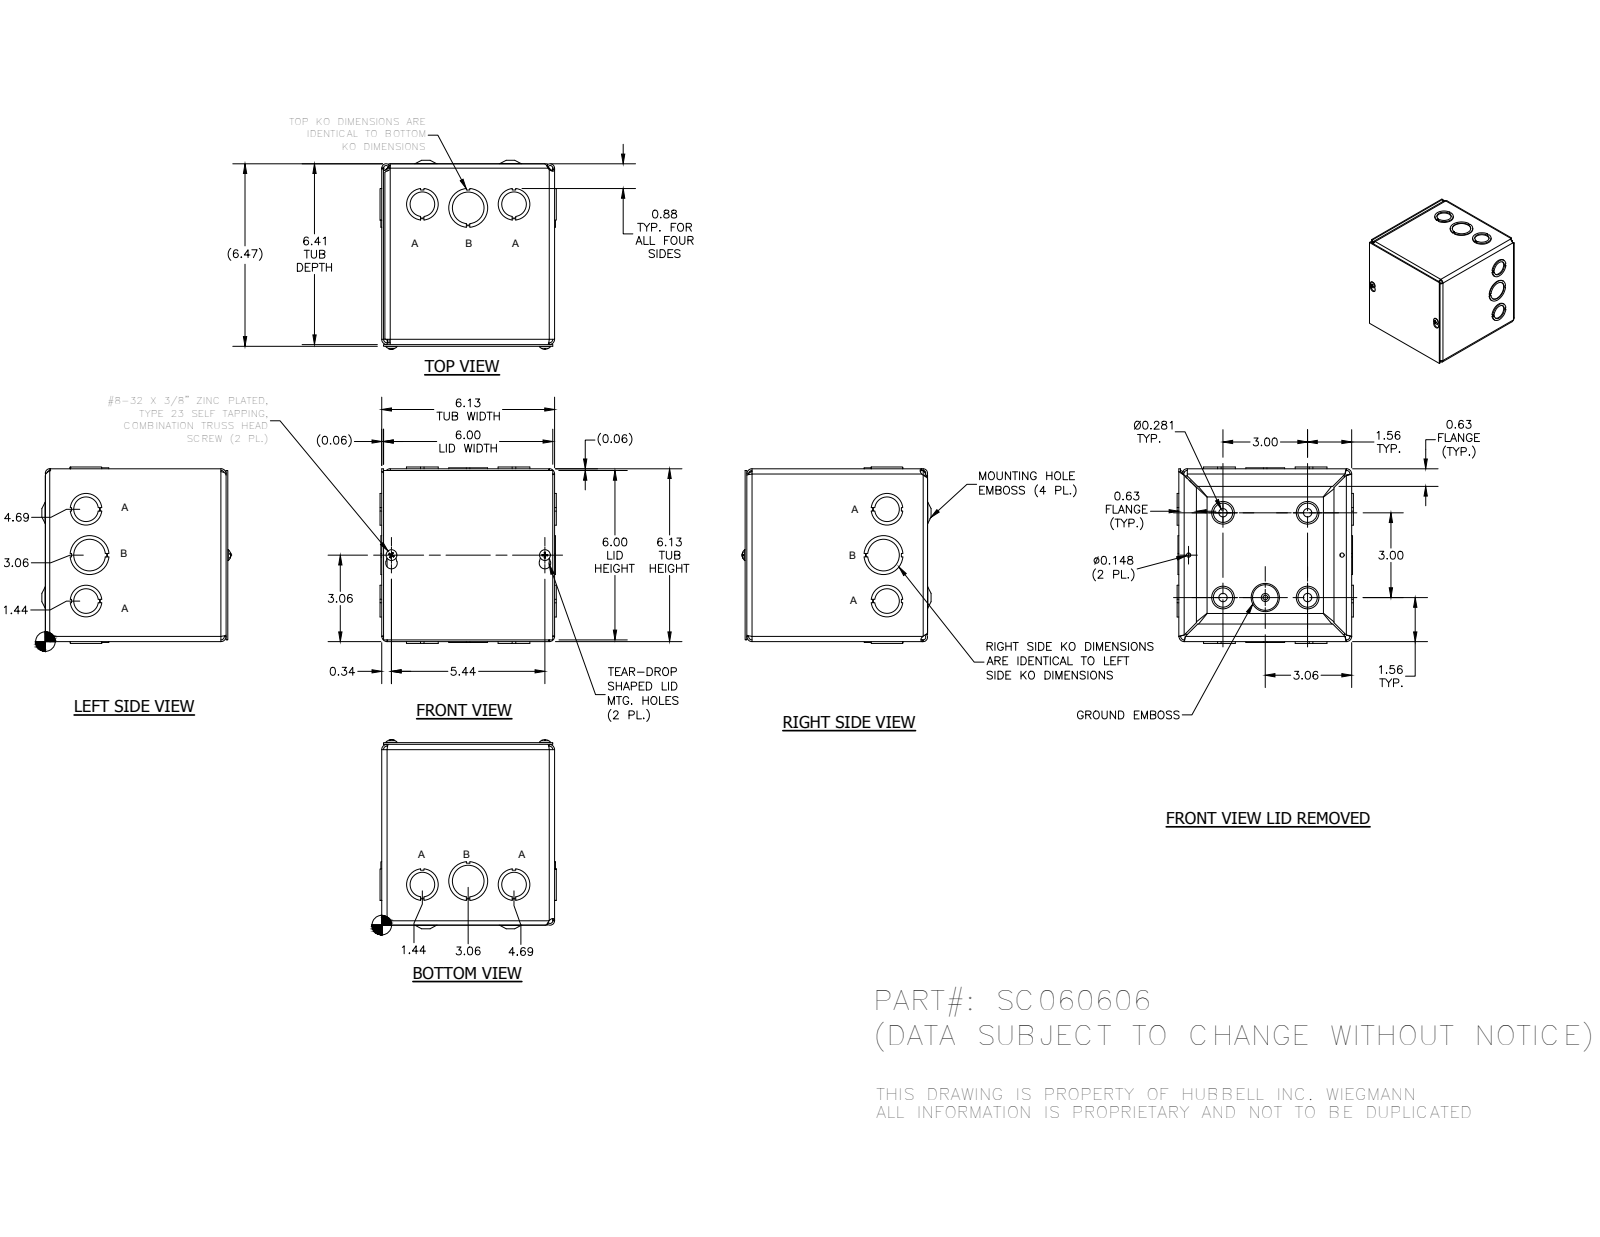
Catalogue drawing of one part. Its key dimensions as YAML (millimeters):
part_name: "SC0606BKP; SC060606WRA; SC0606LID; 34056 (+1 more)"
step_written_by: "Autodesk Inventor 2014 (AUTOMOTIVE_DESIGN)"
units: millimeters
bodies: {solids: 20, faces: 630, planar: 373, cylindrical: 129, other: 128}
overall_size: [170, 158.72, 158.72]
round_holes:
  - {diameter: 28.57, count: 6}
  - {diameter: 7.62, count: 4}
  - {diameter: 22.22, count: 4}
  - {diameter: 3.76, count: 2}
  - {diameter: 34.92, count: 2}
  - {diameter: 4.19, count: 1}
round_bosses_or_shafts:
  - {diameter: 9.75, count: 2}
  - {diameter: 4.17, count: 2}
  - {diameter: 5.8, count: 1}
partial_cylinders:
  - {radius: 3.17, count: 10}
  - {radius: 4.75, count: 8}
  - {radius: 1.4, count: 4}
  - {radius: 1.57, count: 4}
  - {radius: 2.38, count: 4}
  - {radius: 2.97, count: 4}
  - {radius: 3.15, count: 4}
  - {radius: 3.96, count: 4}
face_to_face_distances: [1.57, 1.58, 155.58, 154, 154.01, 152.43, 161.12, 162.69, 1.59, 162.71]
hole_center_spacings: [49.09, 76.2, 38.1, 41.39, 41.4, 82.55, 85.19, 107.76]
